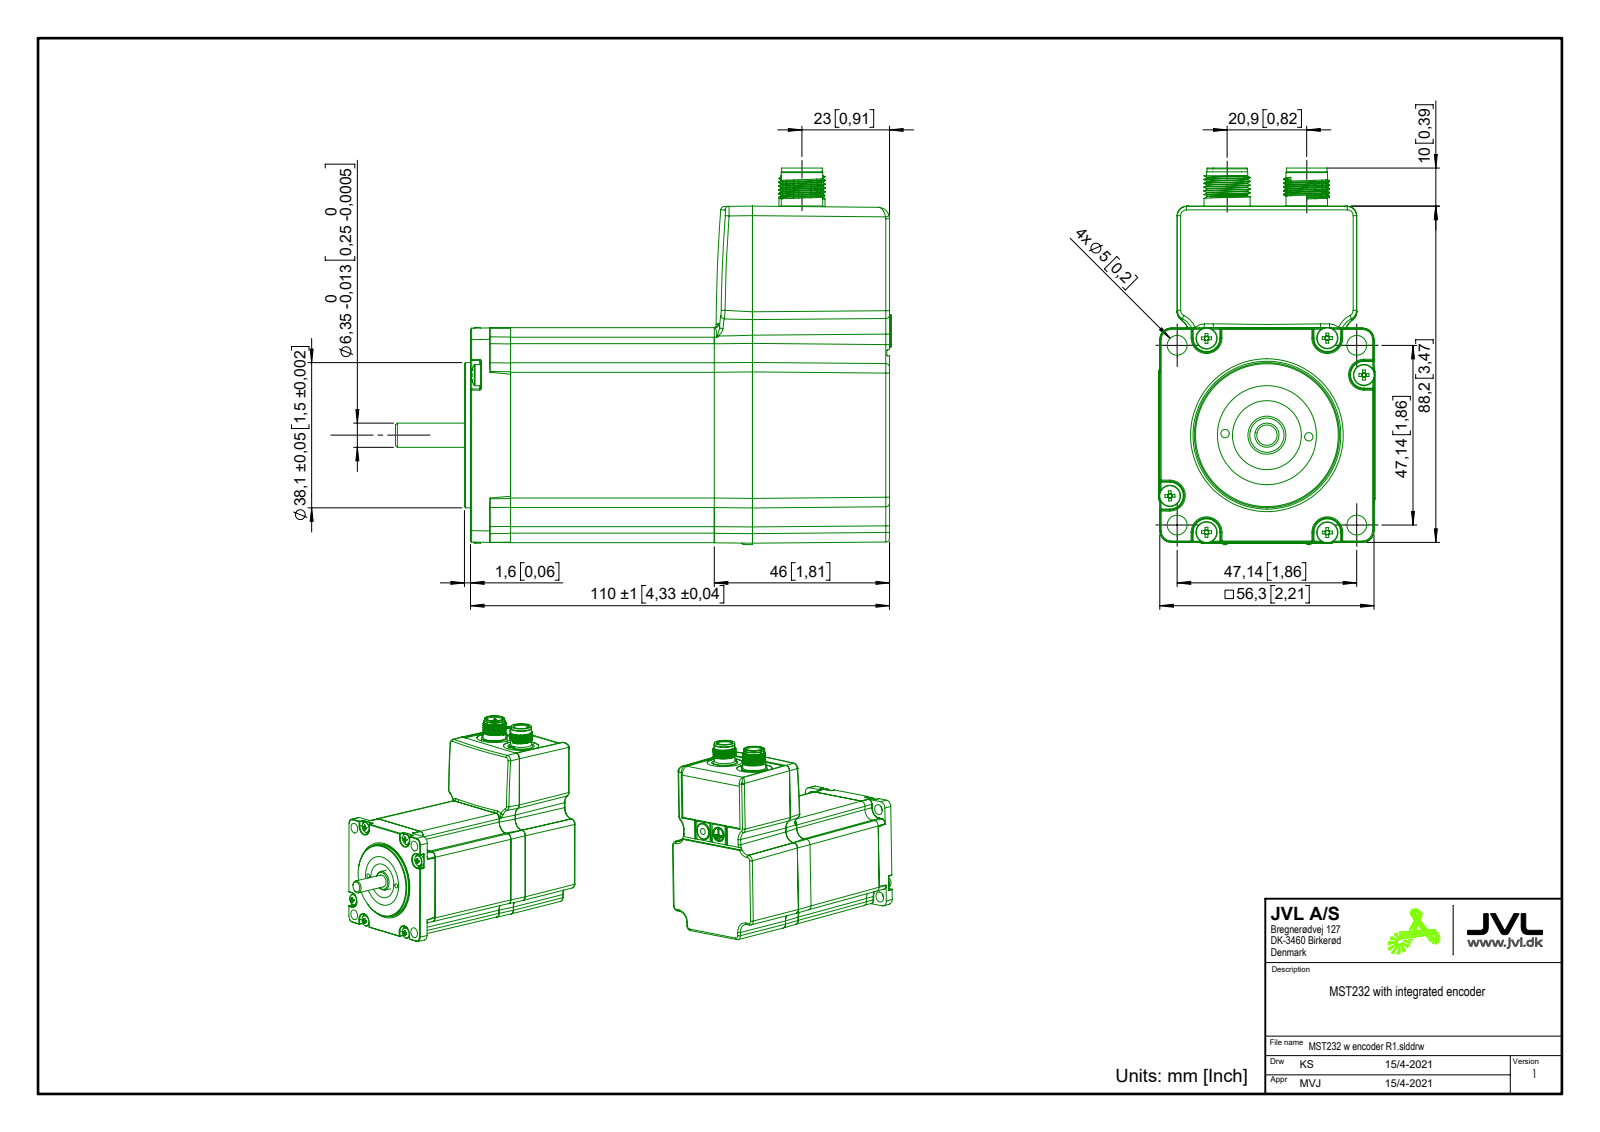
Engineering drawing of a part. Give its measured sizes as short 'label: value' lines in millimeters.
name: MST232 w encoder R1
written by: SolidWorks 2020 (AUTOMOTIVE_DESIGN)
unit: mm
bodies: 1 solid, 1221 faces (389 planar, 304 cylindrical, 528 other)
size: 130.2 × 98.83 × 56.67
volume: 381 372 mm³; area: 40 687 mm²
holes: 8× ⌀1.1, 6× ⌀2.5, 2× ⌀2.2, 2× ⌀18.5, 1× ⌀3.3, 1× ⌀6.76, 1× ⌀8.2, 1× ⌀8.3, 1× ⌀18.1, 1× ⌀26
bosses: 8× ⌀0.8, 6× ⌀5.6, 6× ⌀3, 5× ⌀1, 1× ⌀38.1, 1× ⌀12.1, 1× ⌀12.1, 1× ⌀10.9
rounds: 34× R0.2, 29× R2.5, 18× R5, 16× R0.3, 11× R1, 8× R2.3, 5× R3, 4× R0.8
face distances: 56.4, 4.75, 110, 0.7, 109.3, 51.92, 9.2, 47.2, 56.67, 1.6
hole spacings: 2.74, 30, 2.75, 42.43, 2.32, 4.21, 60, 2.33
